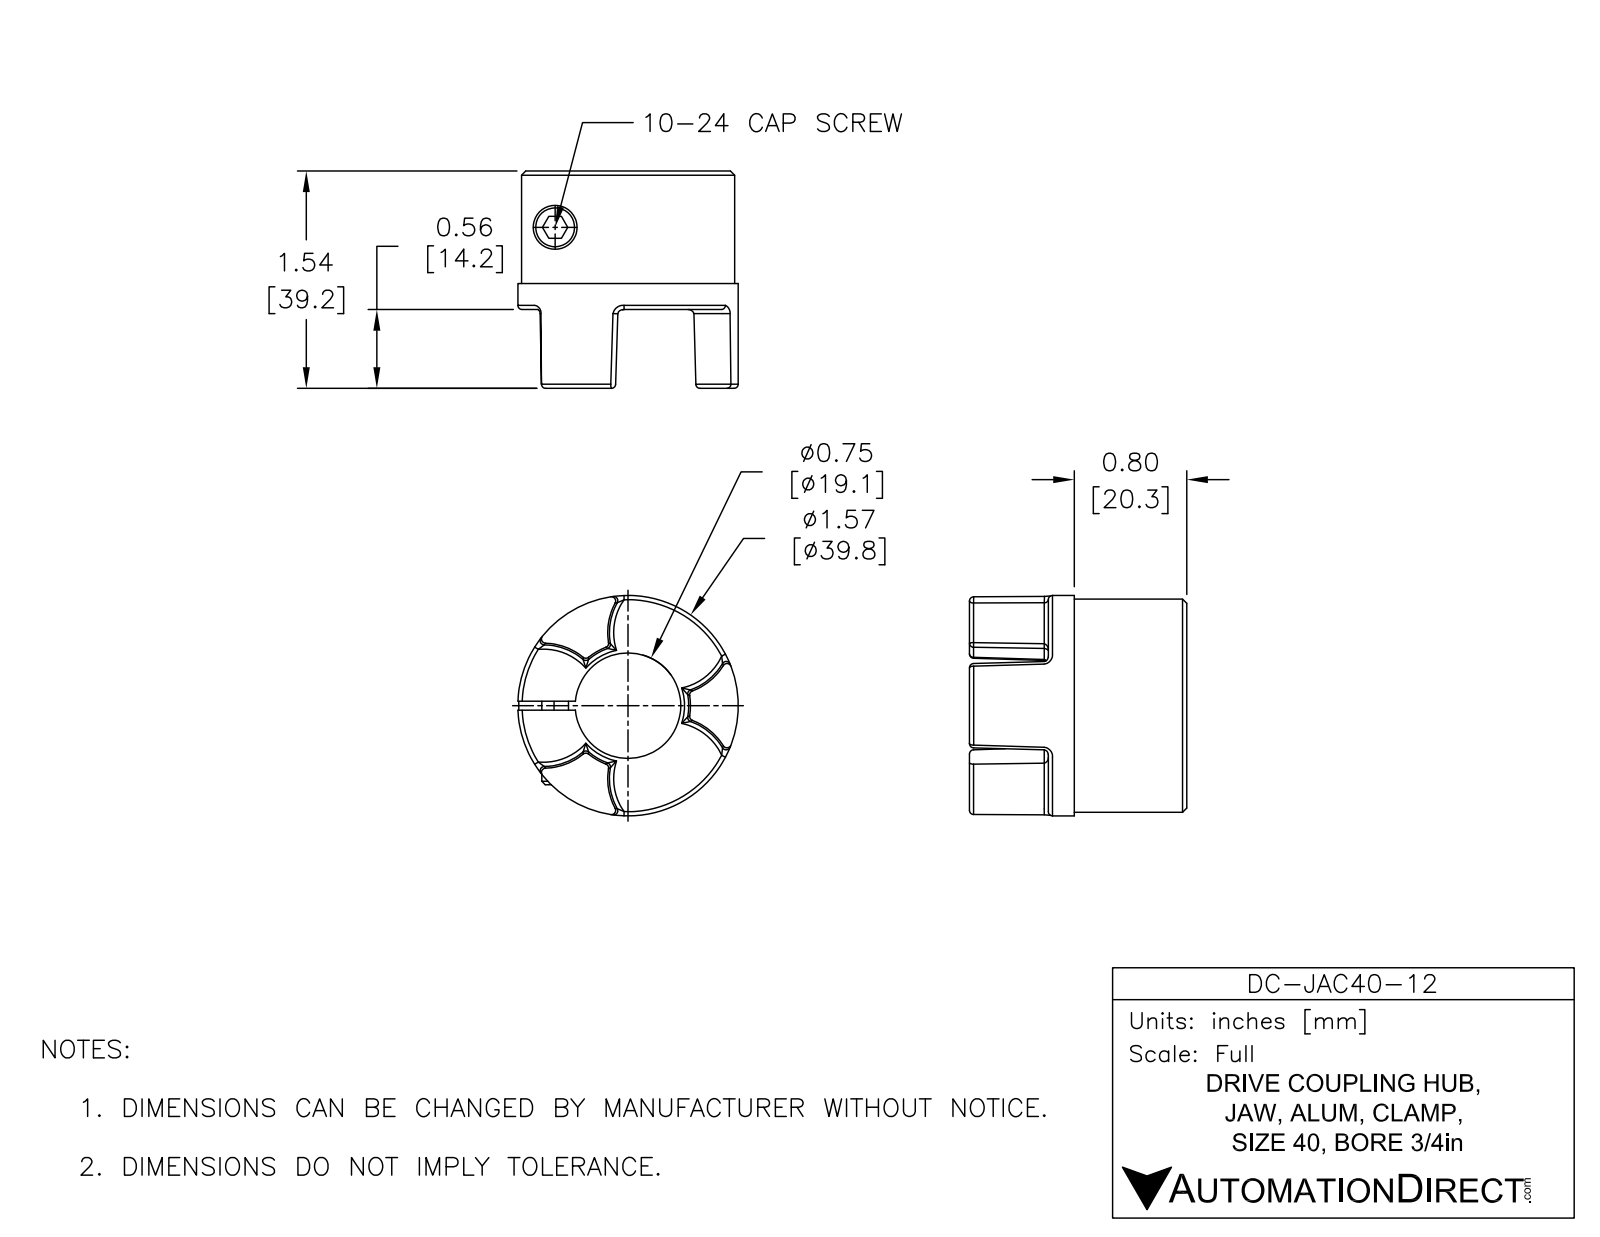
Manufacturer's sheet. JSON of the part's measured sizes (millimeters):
{"part_name": "DC-JAC40-12", "step_written_by": "SolidWorks 2015 (AUTOMOTIVE_DESIGN)", "units": "millimeters", "bodies": {"solids": 1, "faces": 105, "planar": 11, "cylindrical": 17, "other": 77}, "overall_size": [39.78, 39.76, 39.22], "volume_mm3": 24803, "surface_area_mm2": 8740, "round_holes": [[5.11, 1], [8.36, 1], [19.05, 1]], "round_bosses_or_shafts": [[39.78, 1], [38.48, 1]], "partial_cylinders_radius": [[10.94, 1], [12.13, 1]], "face_to_face_distances": [24.99, 1.6, 39.22, 14.23, 20.29, 4.7, 18.93, 3.99, 5.59, 25.03]}
